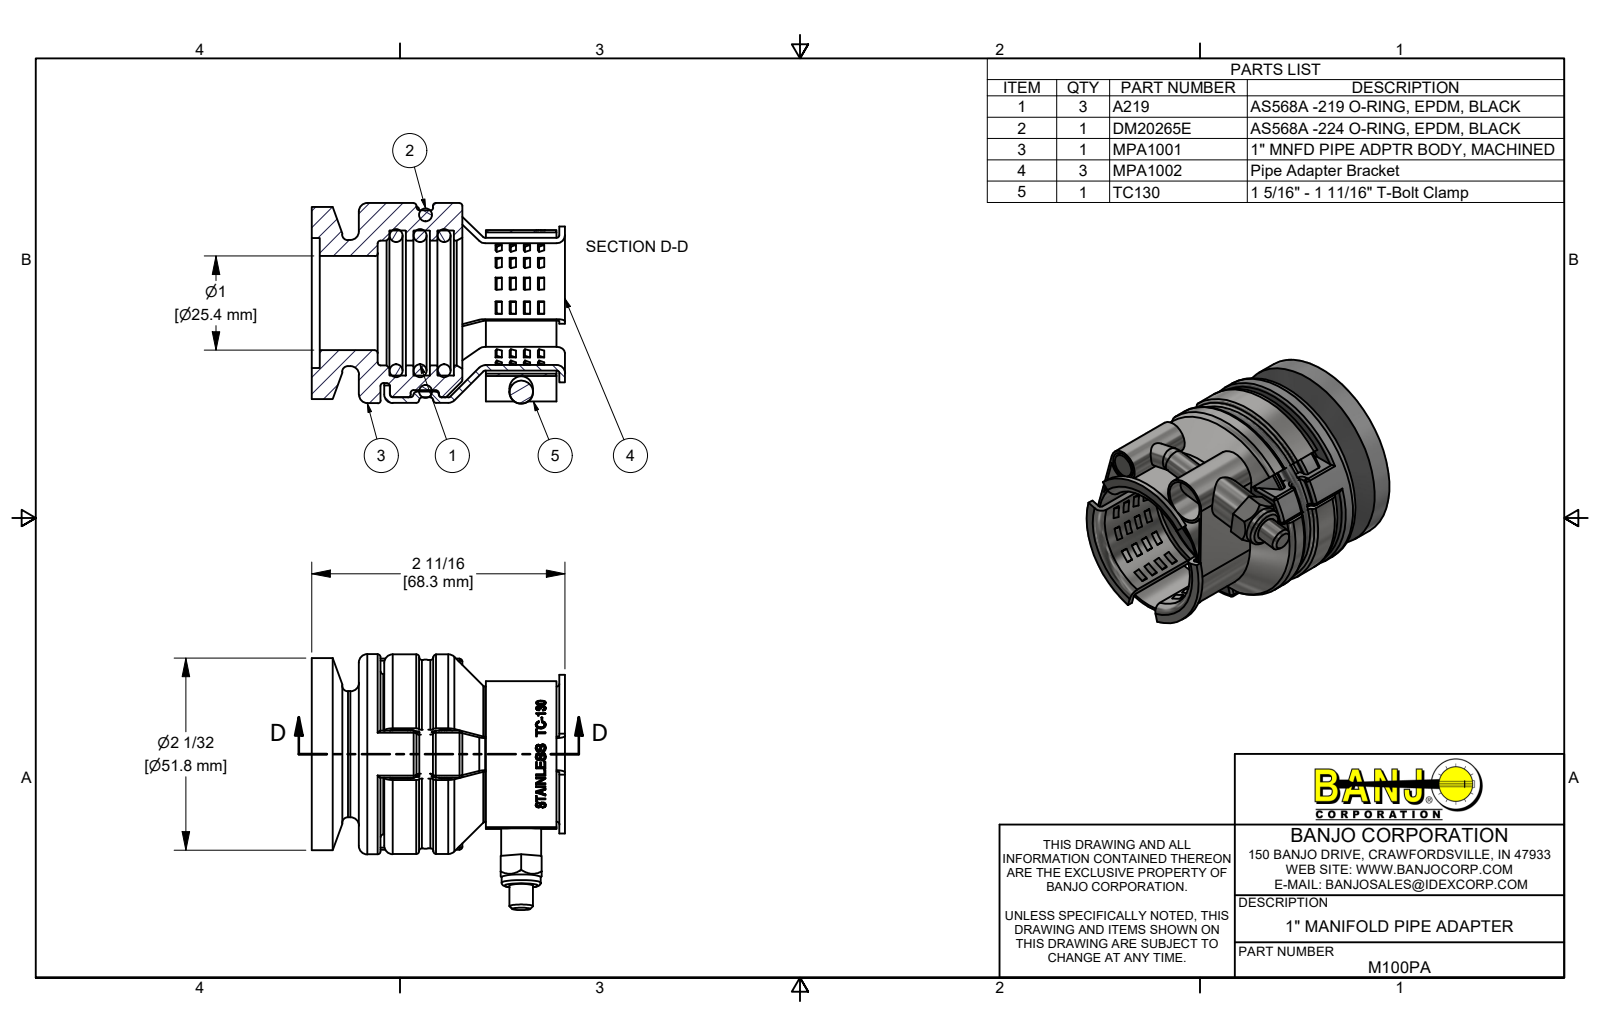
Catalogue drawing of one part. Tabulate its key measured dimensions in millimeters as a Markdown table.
| quantity | value |
| --- | --- |
| part name | M100PA; MPA1001; MPA1001X; MPA1002 (+3 more) |
| STEP written by | Autodesk Inventor 2021 (AUTOMOTIVE_DESIGN) |
| units | millimeters |
| bodies | 9 solids, 923 faces (340 planar, 135 cylindrical, 448 other) |
| overall size | 69 × 68.3 × 55.4 |
| volume | 60 600 mm³ |
| surface area | 47 500 mm² |
| round holes (diameter × count) | 7.6 × 1, 11.4 × 1, 25.4 × 1, 33.7 × 1, 35.1 × 1, 38.1 × 1 |
| round bosses / shafts (diameter × count) | 54 × 1, 51.8 × 1, 50.8 × 1, 47 × 1, 39.4 × 1, 39.1 × 1, 34 × 1, 12.7 × 1 |
| partial cylindrical surfaces (radius × count) | 0.8 × 27, 16.7 × 1, 18.2 × 1, 21.4 × 1, 21.6 × 1, 22.2 × 1, 23.9 × 1, 25 × 1 |
| main face-to-face distances | 12.7, 19.6, 6.5, 21.1, 5.8, 40.6, 6.9, 2, 8.4, 6.4 |
| hole center spacings | 23.5, 24.1, 26 |
